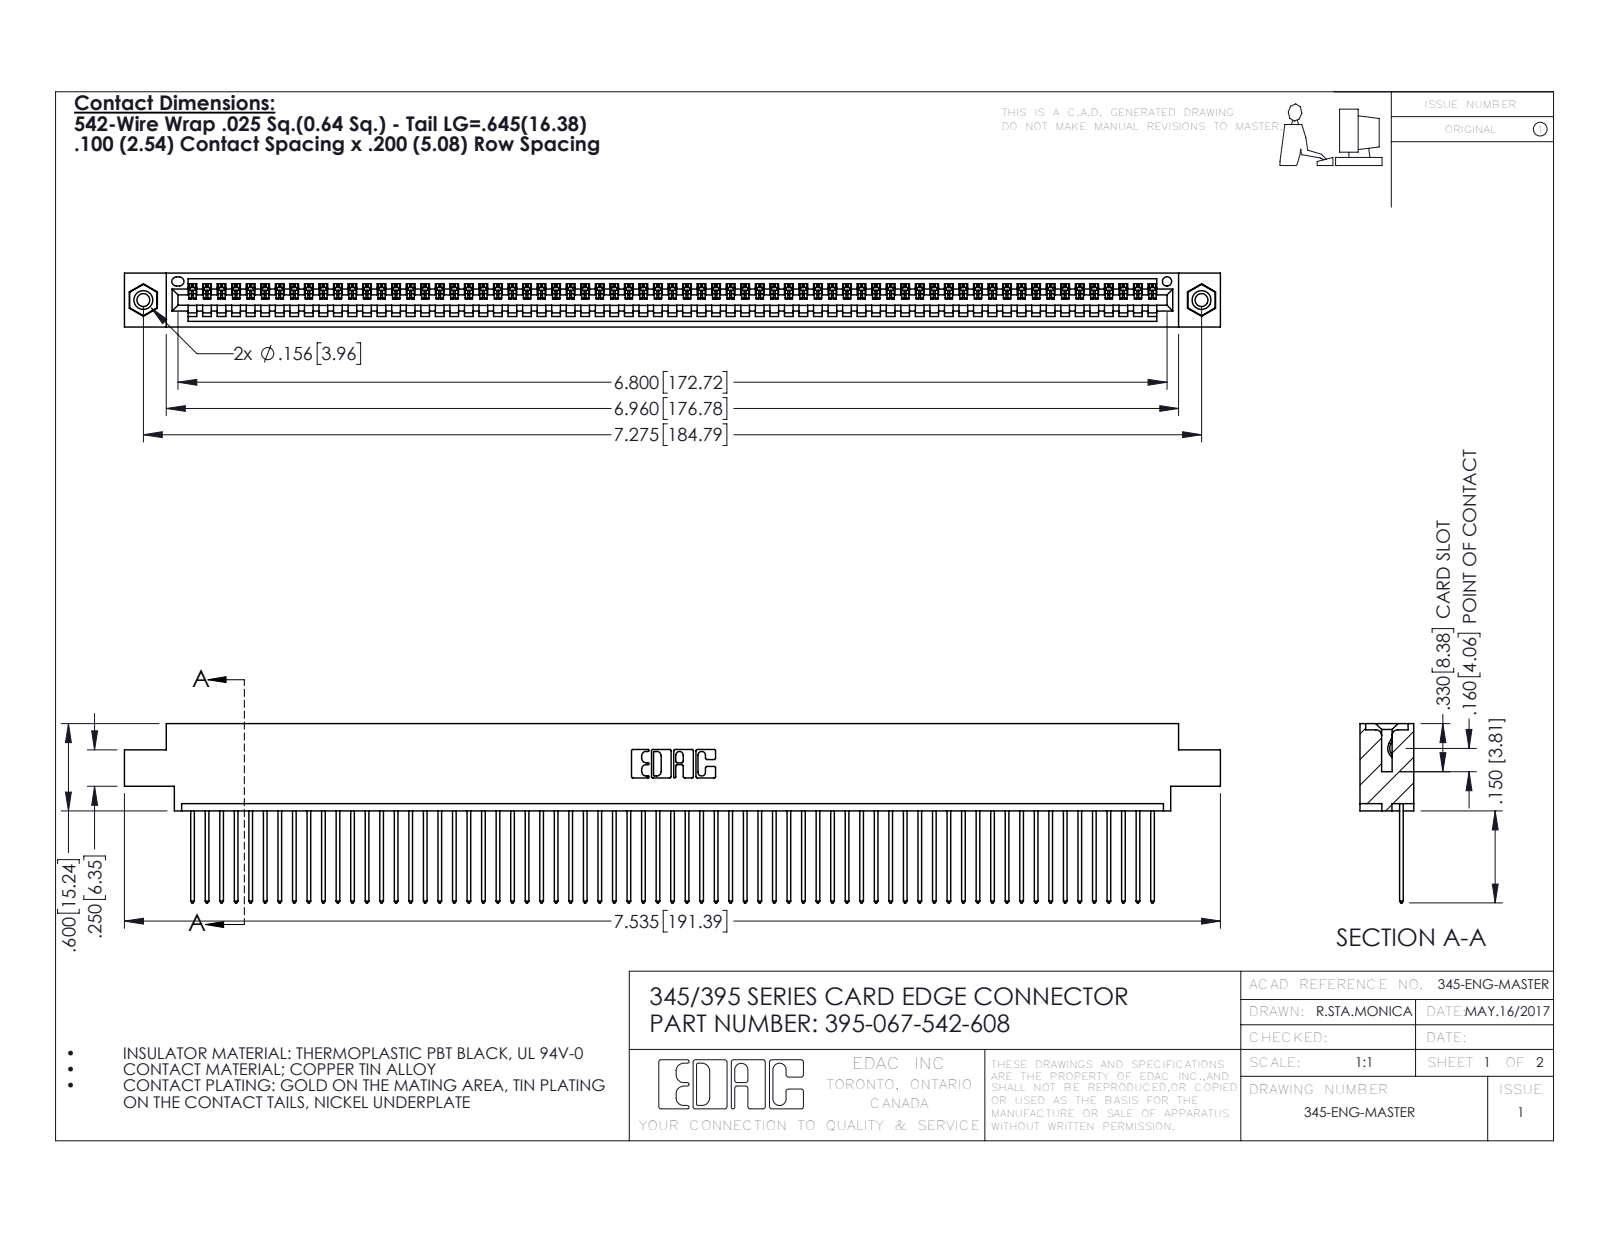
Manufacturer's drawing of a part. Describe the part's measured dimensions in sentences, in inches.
The part is named "345-250-001_345-250-003-102; 345-292-001_345-293-142; 395-067-542-608; 345 Part_0.170 Offset - 0.156 Dia-TI". Its 3-D file was written by "SolidWorks 2016 (CONFIG_CONTROL_DESIGN)". It is 70 solids with 4076 faces: 2796 planar, 1264 cylindrical and 16 other. Overall it measures 7.535 by 1.232 by 0.37 inches. Its volume is 1.124 cubic inches and its surface area 40.14 square inches. Round holes: 2 of diameter 0.089, 2 of diameter 0.125, 2 of diameter 0.156, 1 of diameter 0.064. Round bosses or shafts: 2 of diameter 0.155. Partial cylindrical surfaces (rounded edges, fillets, slot ends): 134 of radius 0.006, 134 of radius 0.01, 22 of radius 0.01, 6 of radius 0.007, 6 of radius 0.031, 3 of radius 0.026, 2 of radius 0.031, 2 of radius 0.04. The main face-to-face distances are 0.072, 0.298, 0.37, 0.098, 0.272, 0.025, 0.2, 0.225, 0.175, 0.149. The hole center spacings are 0.27, 7.039, 7.275.
